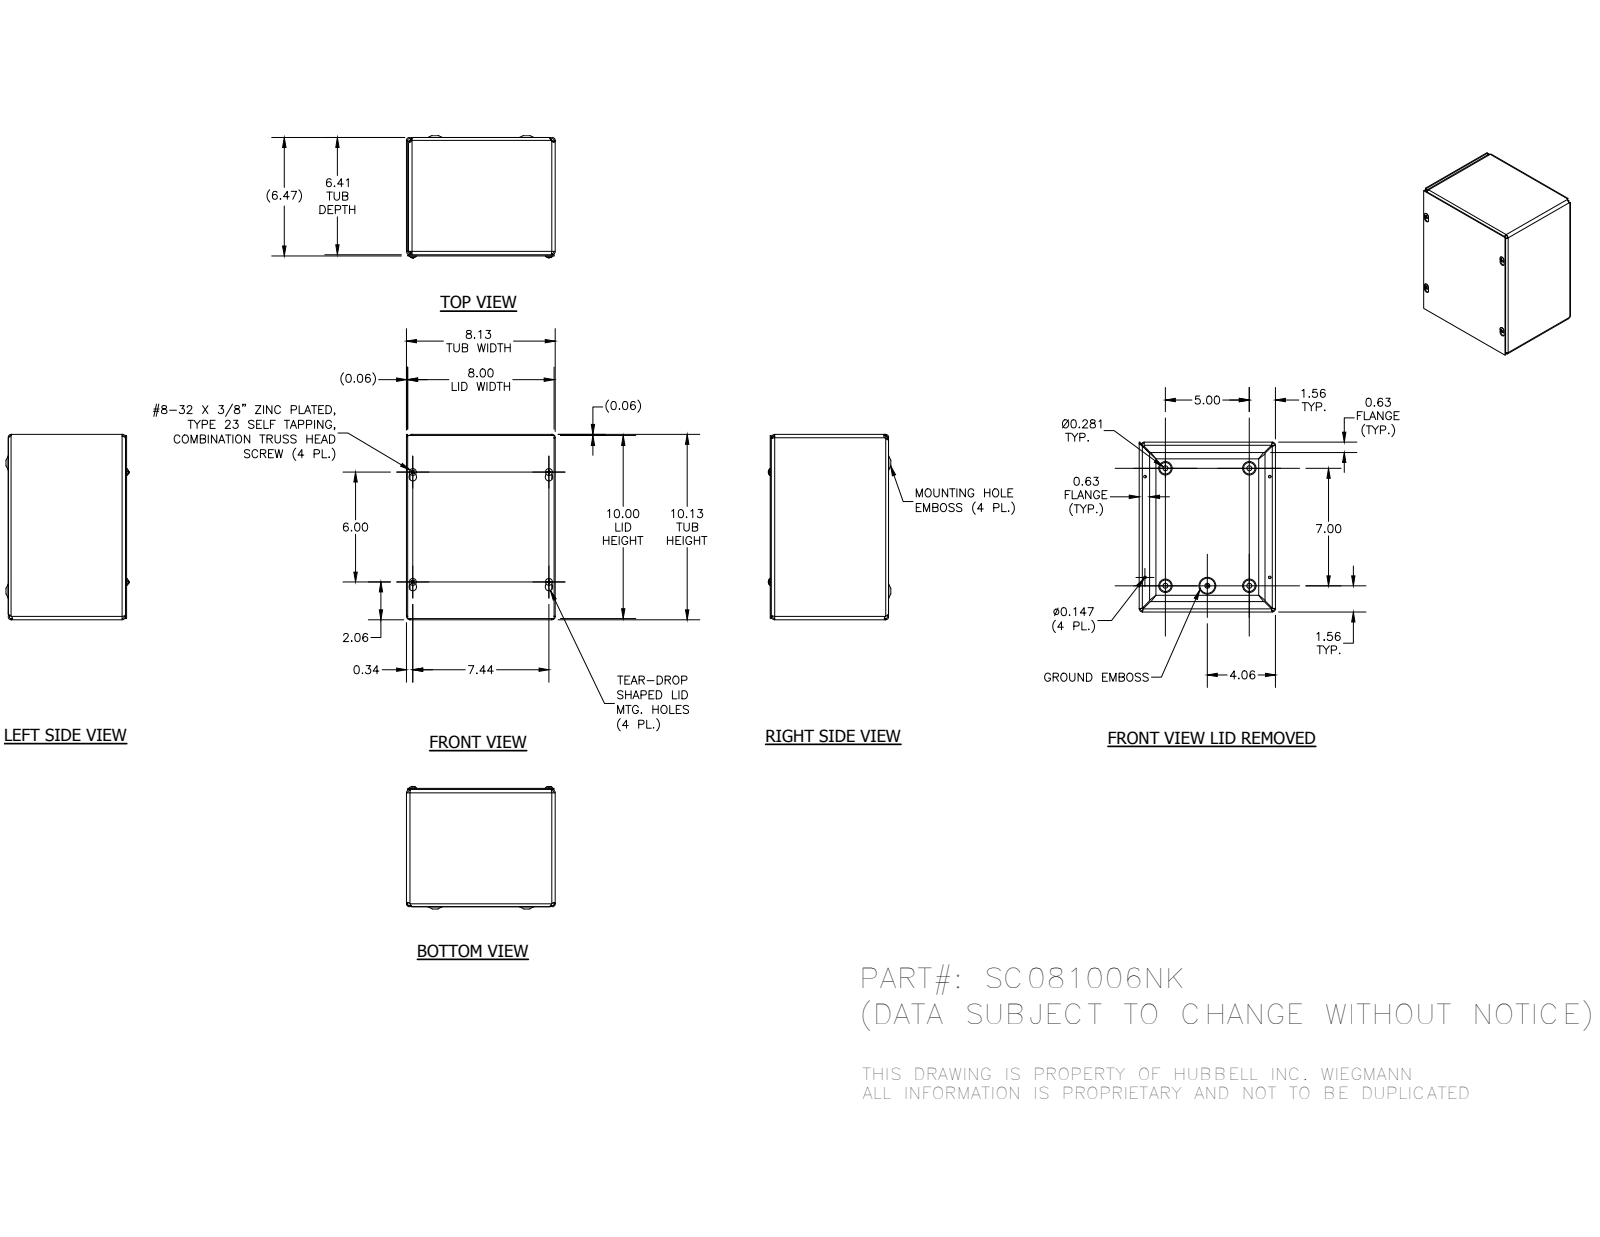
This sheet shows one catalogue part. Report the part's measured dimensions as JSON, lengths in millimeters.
{"part_name": "SC0810BKP; SC081006NKWRA; SC0810LID; 34056 (+1 more)", "step_written_by": "Autodesk Inventor 2014 (AUTOMOTIVE_DESIGN)", "units": "millimeters", "bodies": {"solids": 7, "faces": 357, "planar": 132, "cylindrical": 67, "other": 158}, "overall_size": [257.18, 206.38, 170], "volume_mm3": 439245, "surface_area_mm2": 564626, "round_holes": [[3.73, 4], [7.62, 4], [4.19, 1]], "round_bosses_or_shafts": [[9.75, 4], [4.17, 4], [5.8, 1]], "partial_cylinders_radius": [[3.17, 12], [4.75, 8], [1.4, 4], [1.57, 4], [2.38, 4], [2.97, 4], [3.15, 4], [3.96, 4]], "face_to_face_distances": [1.57, 1.58, 161.12, 162.69, 1.59, 162.71, 164.28, 204.8, 206.38, 203.23], "hole_center_spacings": [167.98, 228.49, 33.45, 33.46, 63.5, 127, 152.4, 158.46]}
